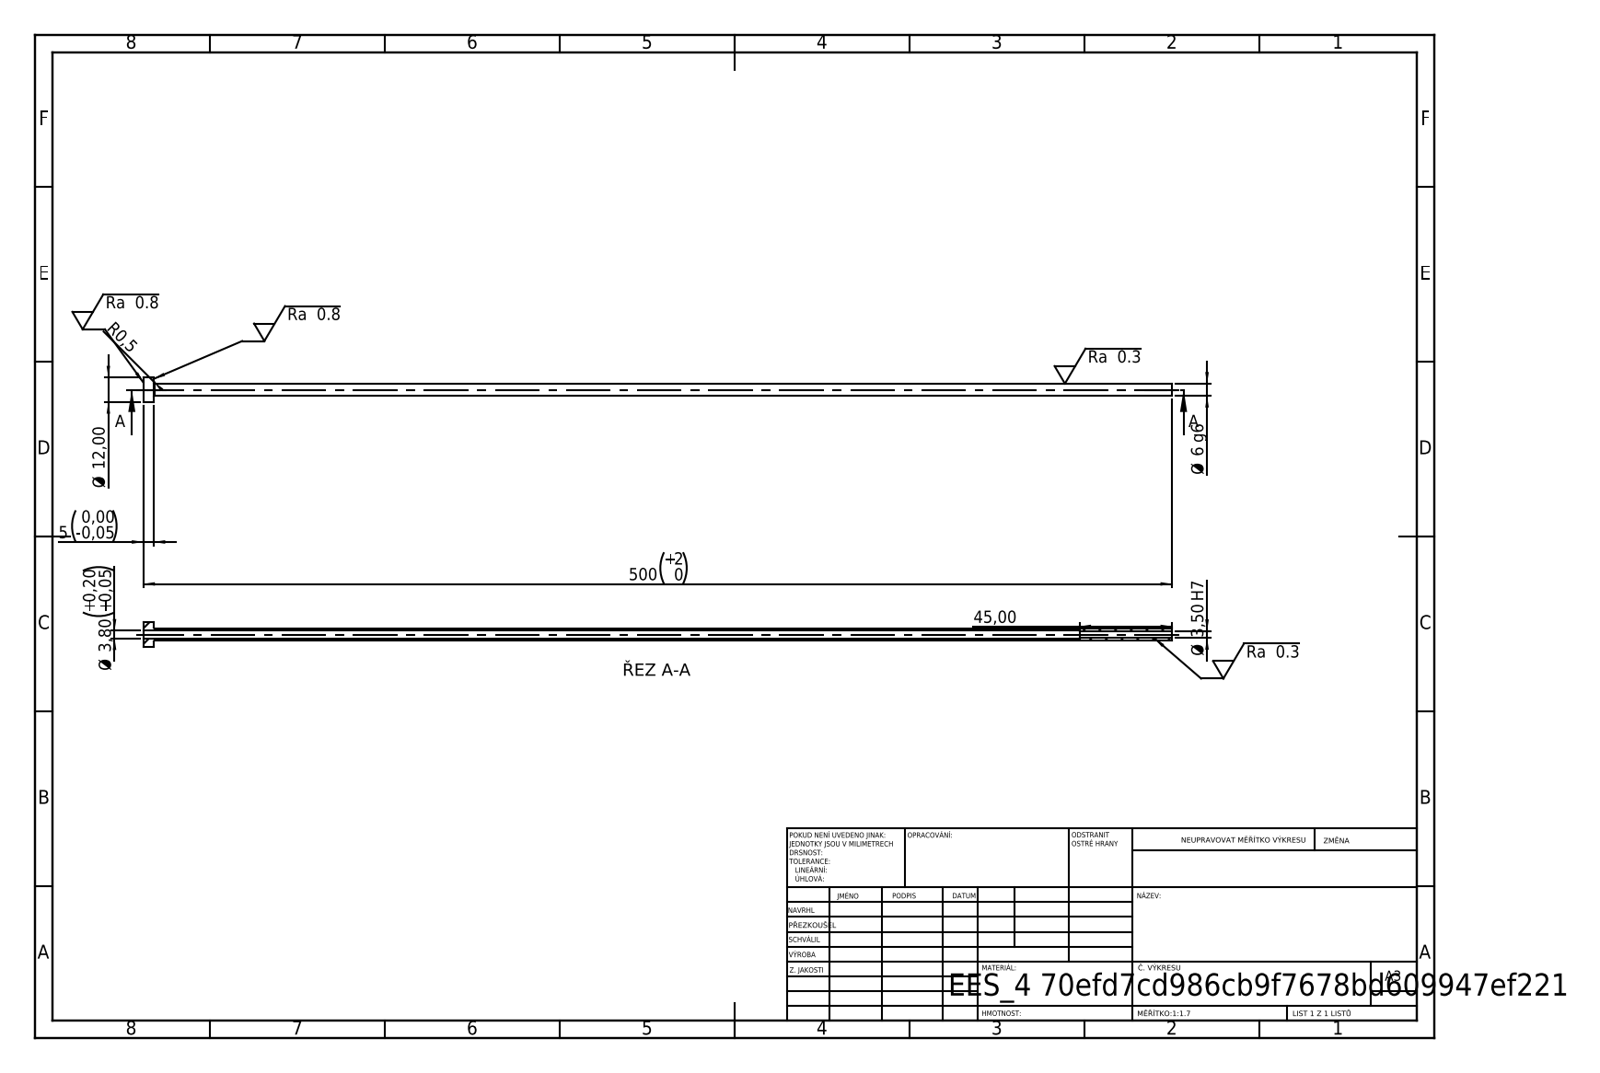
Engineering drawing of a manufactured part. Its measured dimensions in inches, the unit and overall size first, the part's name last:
Units: inches
Overall size (bounding box): 19.685 × 0.472 × 0.472
Round holes (diameter × count): ⌀0.138 ×1, ⌀0.15 ×1
Round bosses / shafts (diameter × count): ⌀0.472 ×1, ⌀0.236 ×1
Main face-to-face distances: 0.197, 19.685, 19.488, 17.913, 17.717, 1.772
Volume: 0.547 in³ · Surface area: 24.26 in²
Bodies: 1 solid, 14 faces (4 planar, 8 cylindrical, 2 other)
STEP written by: SolidWorks 2019 (CONFIG_CONTROL_DESIGN)
